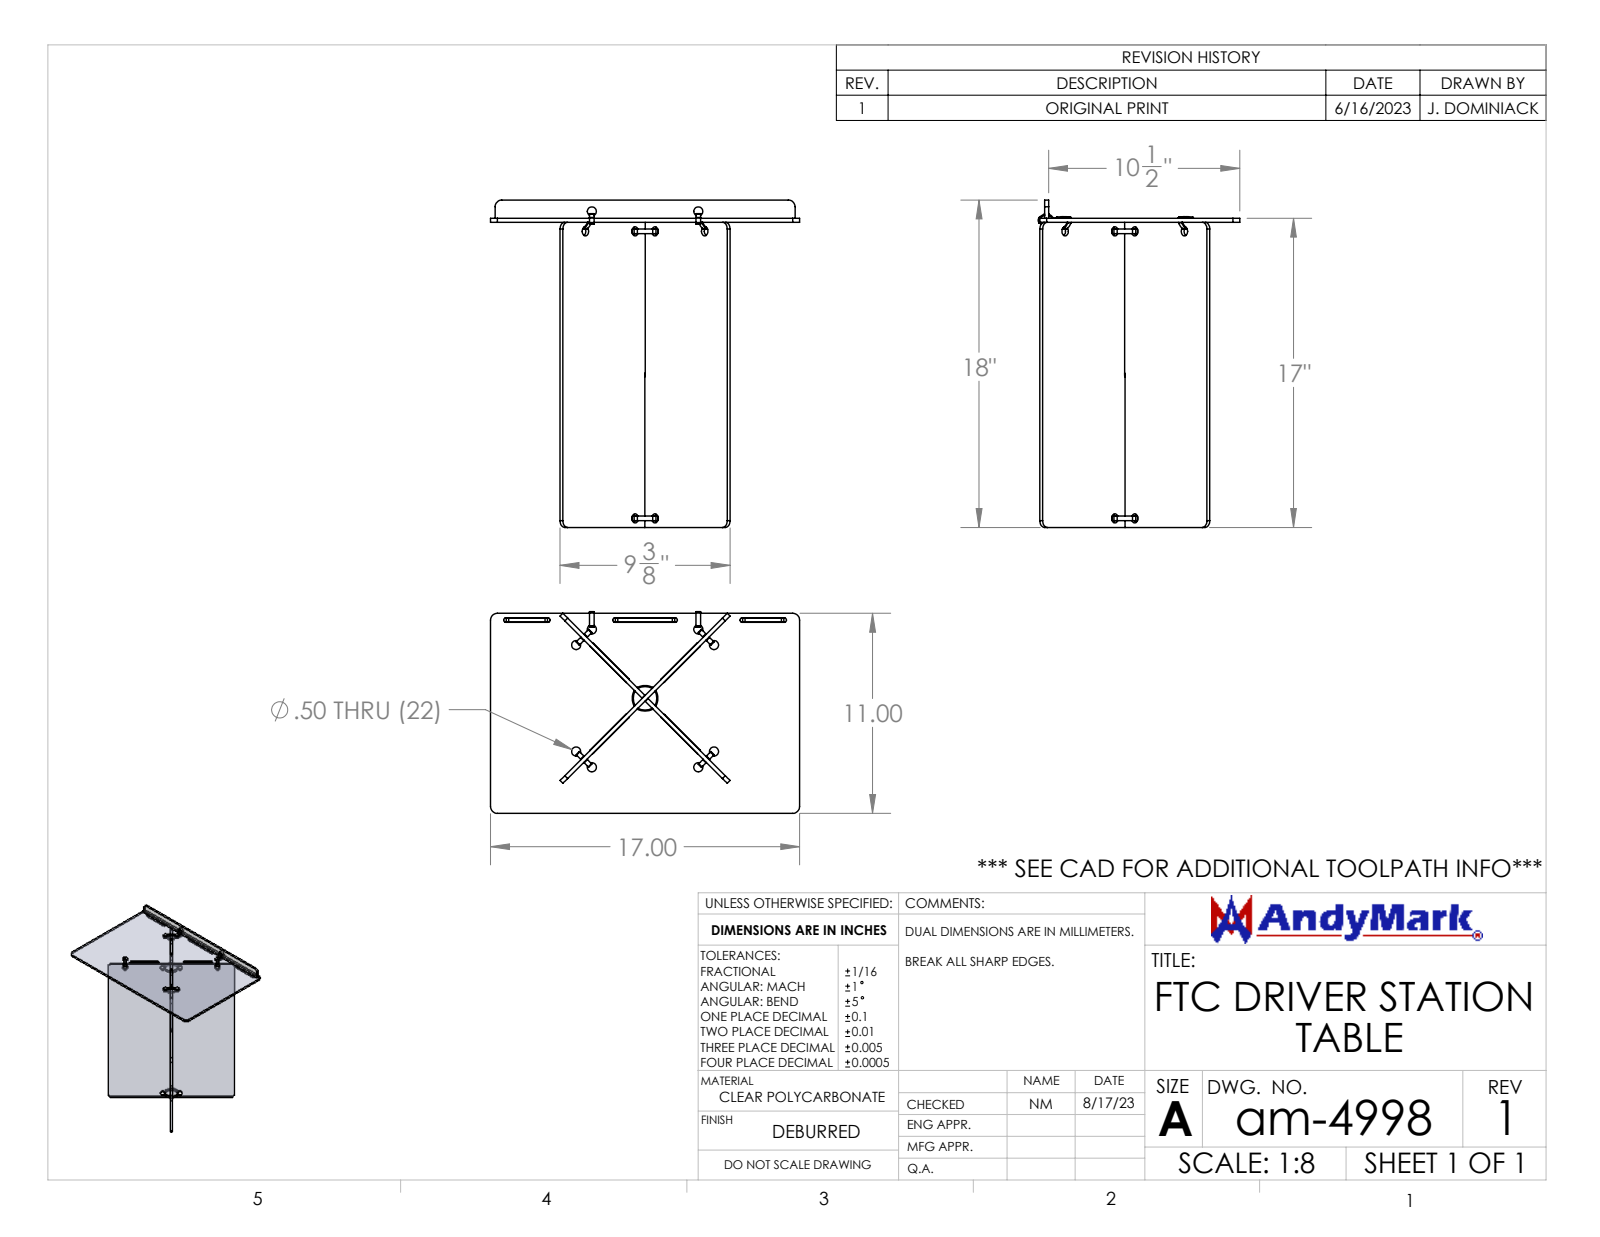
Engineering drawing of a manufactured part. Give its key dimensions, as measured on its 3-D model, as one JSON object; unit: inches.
{"part_name": "am-4998_leg_A FTC Driver Station Table Leg A; Leg Zip Tie; am-4998_shelf Trimmed FTC Driver Station Table Shelf; Wall Zip Tie (+4 more)", "step_written_by": "SolidWorks 2022 (AUTOMOTIVE_DESIGN)", "units": "inches", "bodies": {"solids": 12, "faces": 492, "planar": 200, "cylindrical": 288, "other": 4}, "overall_size": [19.488, 19.488, 18], "volume_in3": 138.8, "surface_area_in2": 1344, "round_holes": [[0.5, 22]], "partial_cylinders_radius": [[0.125, 14], [0.13, 14], [0.375, 14], [0.01, 10], [0.07, 6], [0.26, 6], [0.072, 4], [0.219, 4]], "face_to_face_distances": [0.22, 0.22, 6.39, 6.61, 0.25, 6.372, 6.628, 0.015, 0.235, 13], "hole_center_spacings": [6.773, 9.5, 1.755, 3.872, 5.628, 9.578, 15.78, 15.877]}
